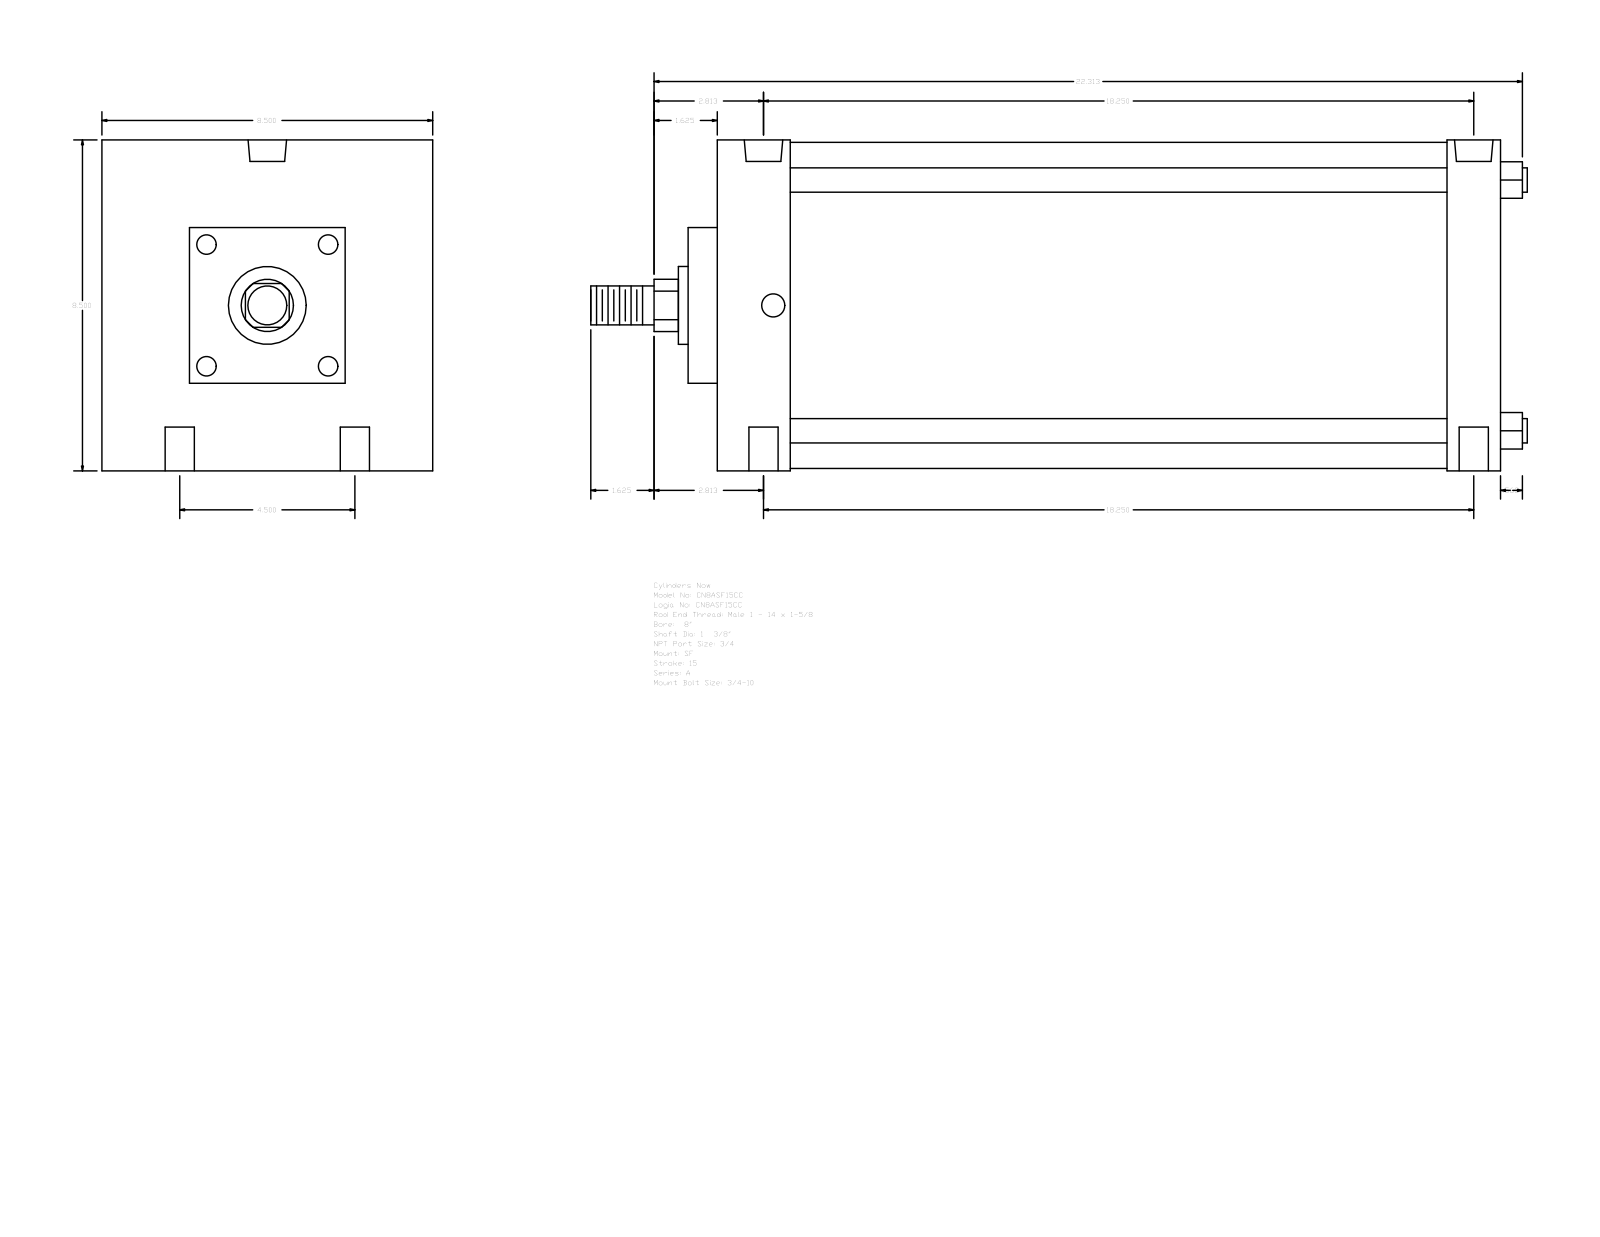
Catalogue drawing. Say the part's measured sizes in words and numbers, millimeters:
The part is named "A_SF__0800_1.375". Its 3-D file was written by "GSSL Pune (CONFIG_CONTROL_DESIGN)". It is 0 solids with 93 faces: 67 planar, 26 cylindrical and 0 other. Overall it measures 611.19 by 215.9 by 215.9 millimeters. Round holes: 4 of diameter 19.05, 2 of diameter 15.08, 2 of diameter 25.12. Round bosses or shafts: 4 of diameter 15.88, 1 of diameter 212.72, 1 of diameter 50.8, 1 of diameter 34.92, 1 of diameter 25.4. Partial cylindrical surfaces (rounded edges, fillets, slot ends): 1 of radius 17.06. The main face-to-face distances are 511.18, 215.9, 47.63, 476.25, 428.62, 463.55, 34.93, 19.04, 66.67, 495.29. The hole center spacings are 57.15, 467.06, 463.55, 114.3, 477.43, 450.85.
